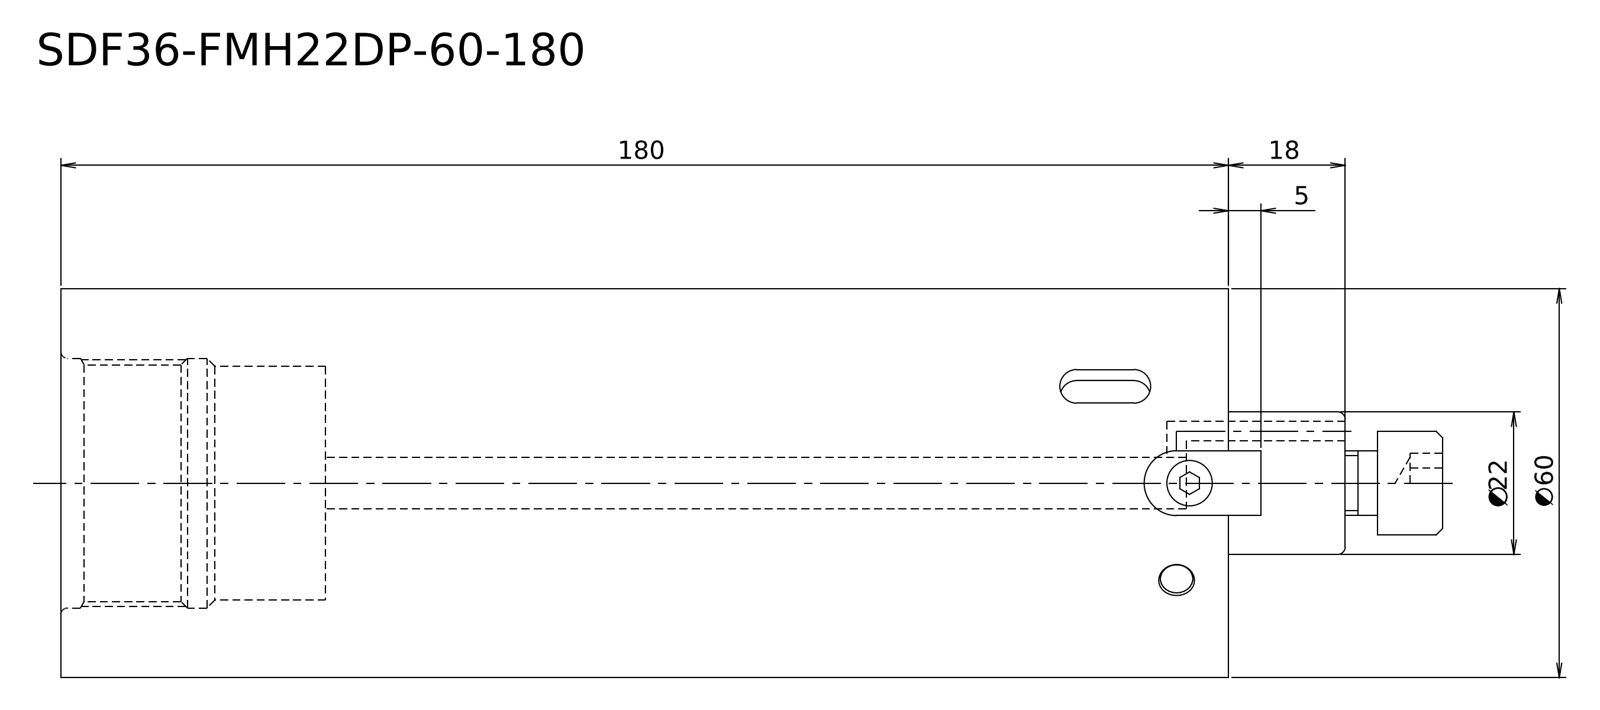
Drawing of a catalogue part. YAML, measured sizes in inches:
step_written_by: "Kubotek KeyCreator V8.5.1 (14335) (CONFIG_CONTROL_DESIGN)"
units: inches
bodies: {solids: 1, faces: 5, planar: 3, cylindrical: 2, other: 0}
overall_size: [7.795, 2.362, 2.362]
volume: 31.47
surface_area: 63.28
round_bosses_or_shafts:
  - {diameter: 2.362, count: 1}
  - {diameter: 0.866, count: 1}
face_to_face_distances: [7.087, 0.709, 7.795]
